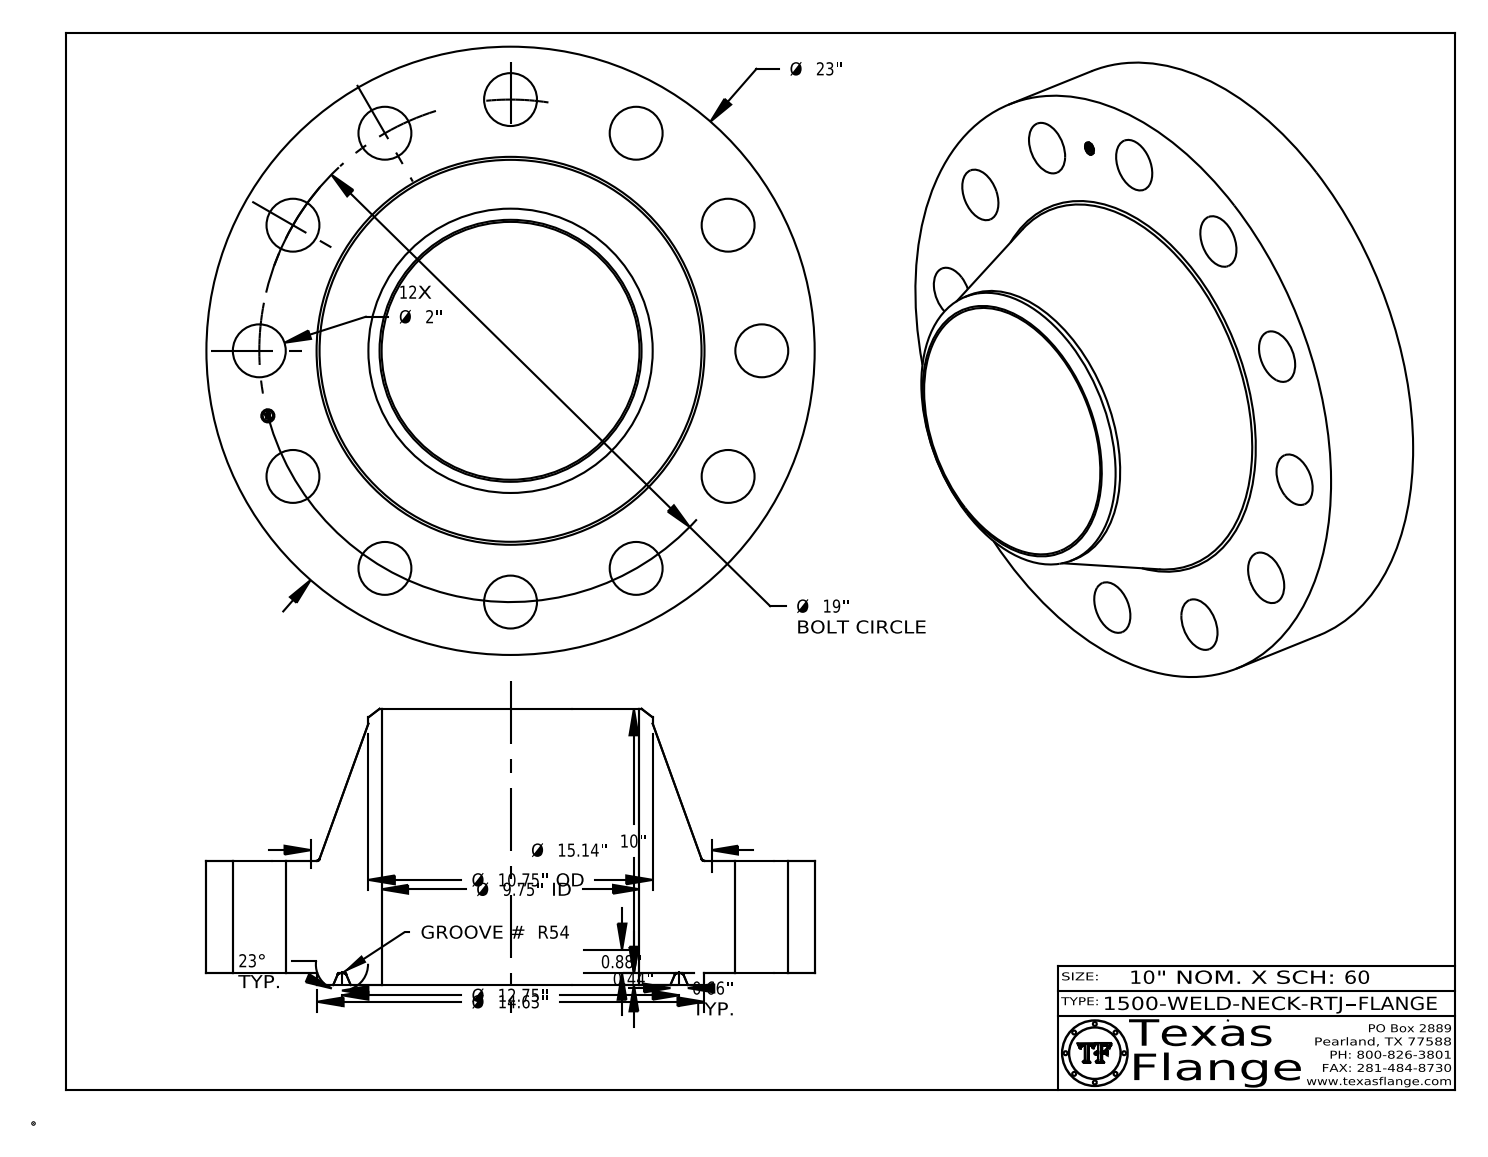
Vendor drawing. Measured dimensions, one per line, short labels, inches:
name: 1500-WELD-NECK-RTJ
written by: CATIA V5 STEP AP214 (AUTOMOTIVE_DESIGN)
unit: in
bodies: 1 solid, 437 faces (371 planar, 52 cylindrical, 14 other)
size: 23 × 23 × 10.438
volume: 1 595 in³; area: 1 751 in²
holes: 12× ⌀2, 1× ⌀0.495, 1× ⌀9.75
bosses: 8× ⌀0.03, 1× ⌀23, 1× ⌀14.625, 1× ⌀10.75, 1× ⌀0.39
face distances: 4.25, 0.438, 4.688, 10.438, 10, 5.75, 4.673, 4.235, 0.015, 5.765
hole spacings: 9.5, 13.435, 16.454, 18.352, 4.918, 19, 4.917, 15.074
